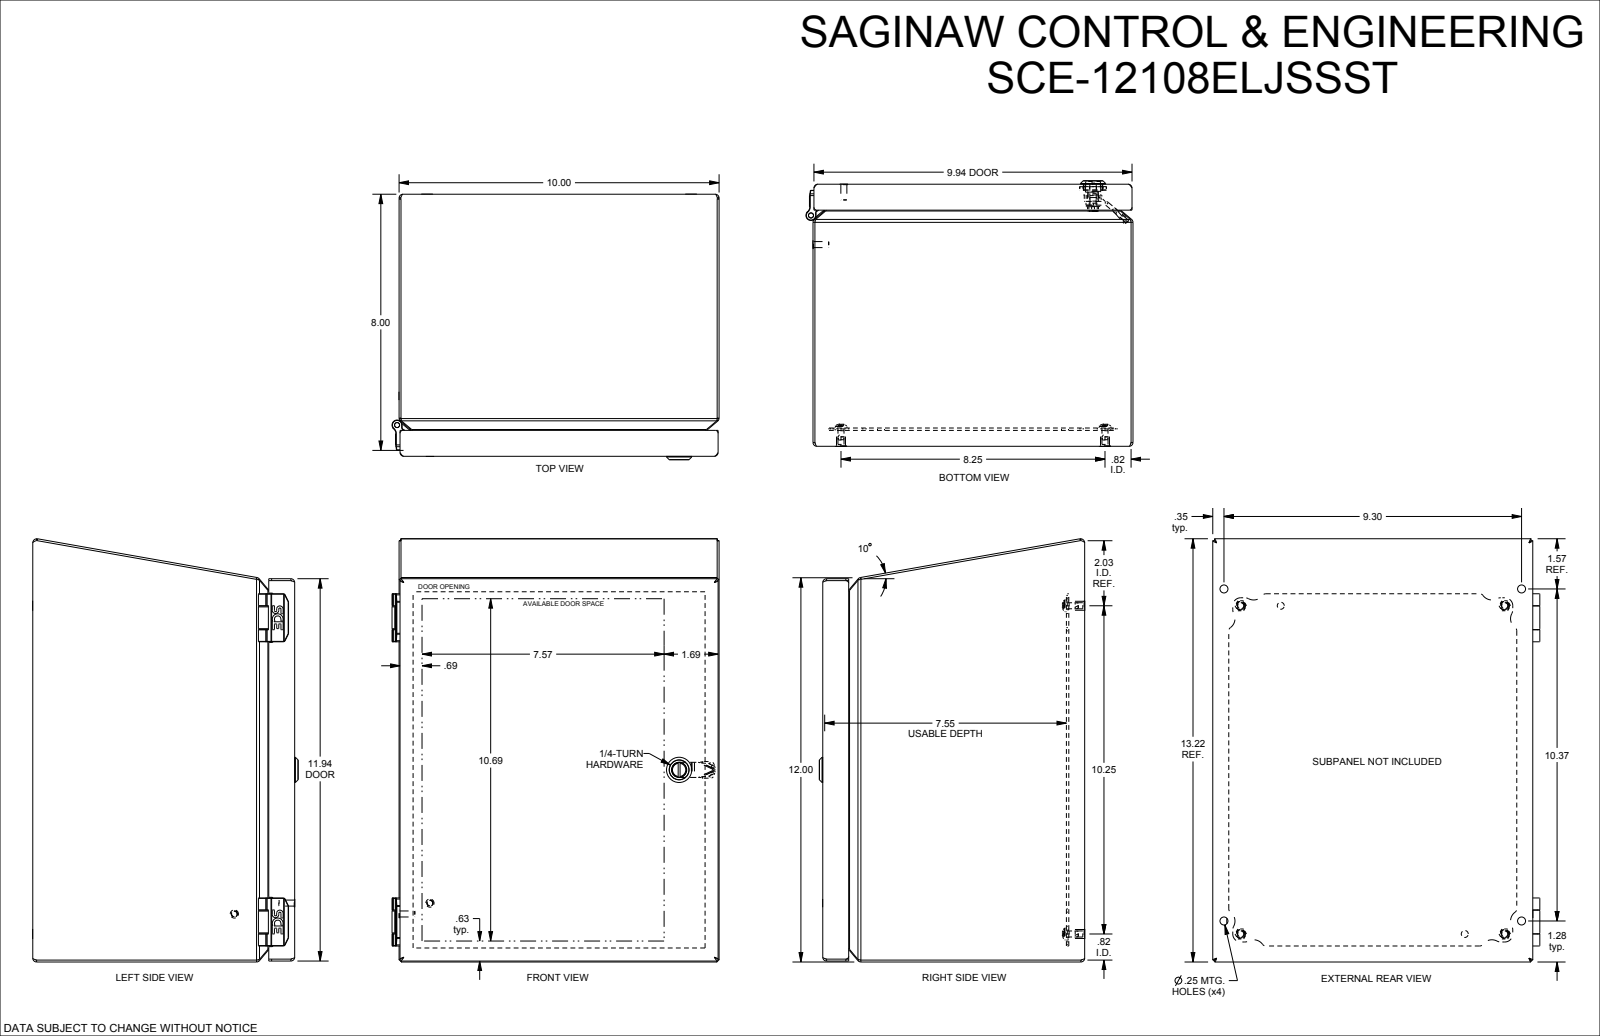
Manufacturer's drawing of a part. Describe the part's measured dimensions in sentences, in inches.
The part is named "SCE-12108ELJSSST". Its 3-D file was written by "SolidWorks 2021 (AUTOMOTIVE_DESIGN)". It is 33 solids with 1454 faces: 566 planar, 353 cylindrical and 535 other. Overall it measures 13.214 by 10.22 by 8.296 inches. Its volume is 20.08 cubic inches and its surface area 1 560 square inches. Round holes: 4 of diameter 0.25, 4 of diameter 0.284, 3 of diameter 0.16, 3 of diameter 0.19, 2 of diameter 0.02, 2 of diameter 0.1, 2 of diameter 0.218, 2 of diameter 0.266, 1 of diameter 0.158, 1 of diameter 0.196, 1 of diameter 0.2, 1 of diameter 0.239. Round bosses or shafts: 6 of diameter 0.188, 5 of diameter 0.16, 4 of diameter 0.373, 4 of diameter 0.28, 4 of diameter 0.237, 3 of diameter 0.483, 2 of diameter 0.26, 2 of diameter 0.256. Partial cylindrical surfaces (rounded edges, fillets, slot ends): 50 of radius 0.03, 24 of radius 0.008, 21 of radius 0.013, 13 of radius 0.25, 11 of radius 0.125, 10 of radius 0.01, 10 of radius 0.06, 8 of radius 0.344. The main face-to-face distances are 0.059, 9.941, 0.06, 8.185, 8.126, 8.125, 8.066, 0.571, 0.512, 7.554. The hole center spacings are 9.5, 0.018, 0.663, 0.743, 1.25, 5.138, 7, 8.25.
